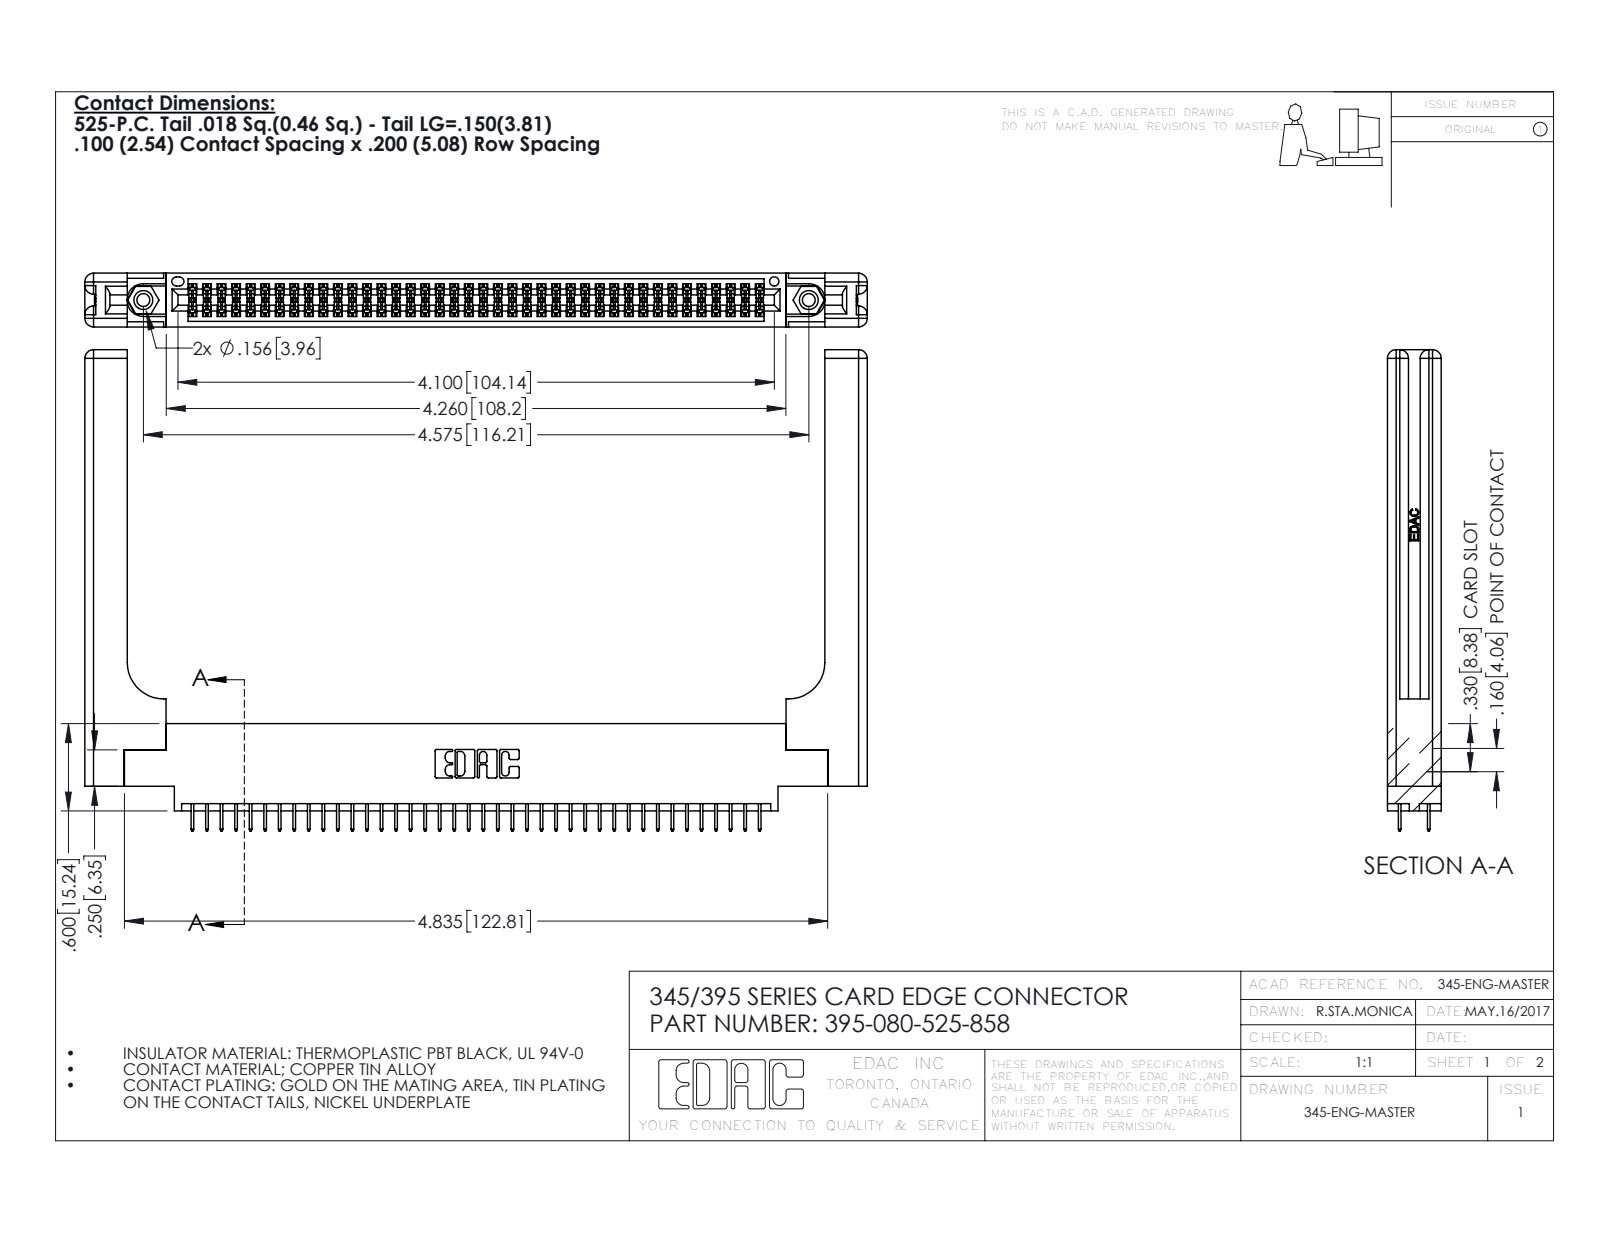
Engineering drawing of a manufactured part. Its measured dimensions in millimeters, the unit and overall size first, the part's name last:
Units: millimetres
Overall size (bounding box): 136.6 × 84 × 9.4
Round holes (diameter × count): ⌀2.3 ×2, ⌀3.2 ×2, ⌀4 ×2, ⌀1.6 ×1
Round bosses / shafts (diameter × count): ⌀3.9 ×2
Partial cylindrical surfaces — rounded edges, fillets, slot ends (radius × count): R0.2 ×120, R0.3 ×22, R1.5 ×16, R0.2 ×6, R0.8 ×6, R0.7 ×3, R0.4 ×2, R0.5 ×2
Main face-to-face distances: 9.4, 1.8, 7.6, 2.5, 6.9, 0.6, 5.1, 5.7, 3.8, 3.8
Hole centre spacings: 6.9, 110.2, 116.2
Volume: 21 480 mm³ · Surface area: 23 990 mm²
Bodies: 85 solids, 4706 faces (3352 planar, 1294 cylindrical, 60 other)
Part name (STEP PRODUCT): 345-220-058_345-220-058; 345-292-001_345-293-125; 345 Part_0.170 Offset - 0.156 Dia-TH; 345-250-001_345-250-001-102 (+1 more)
STEP written by: SolidWorks 2020 (CONFIG_CONTROL_DESIGN)
